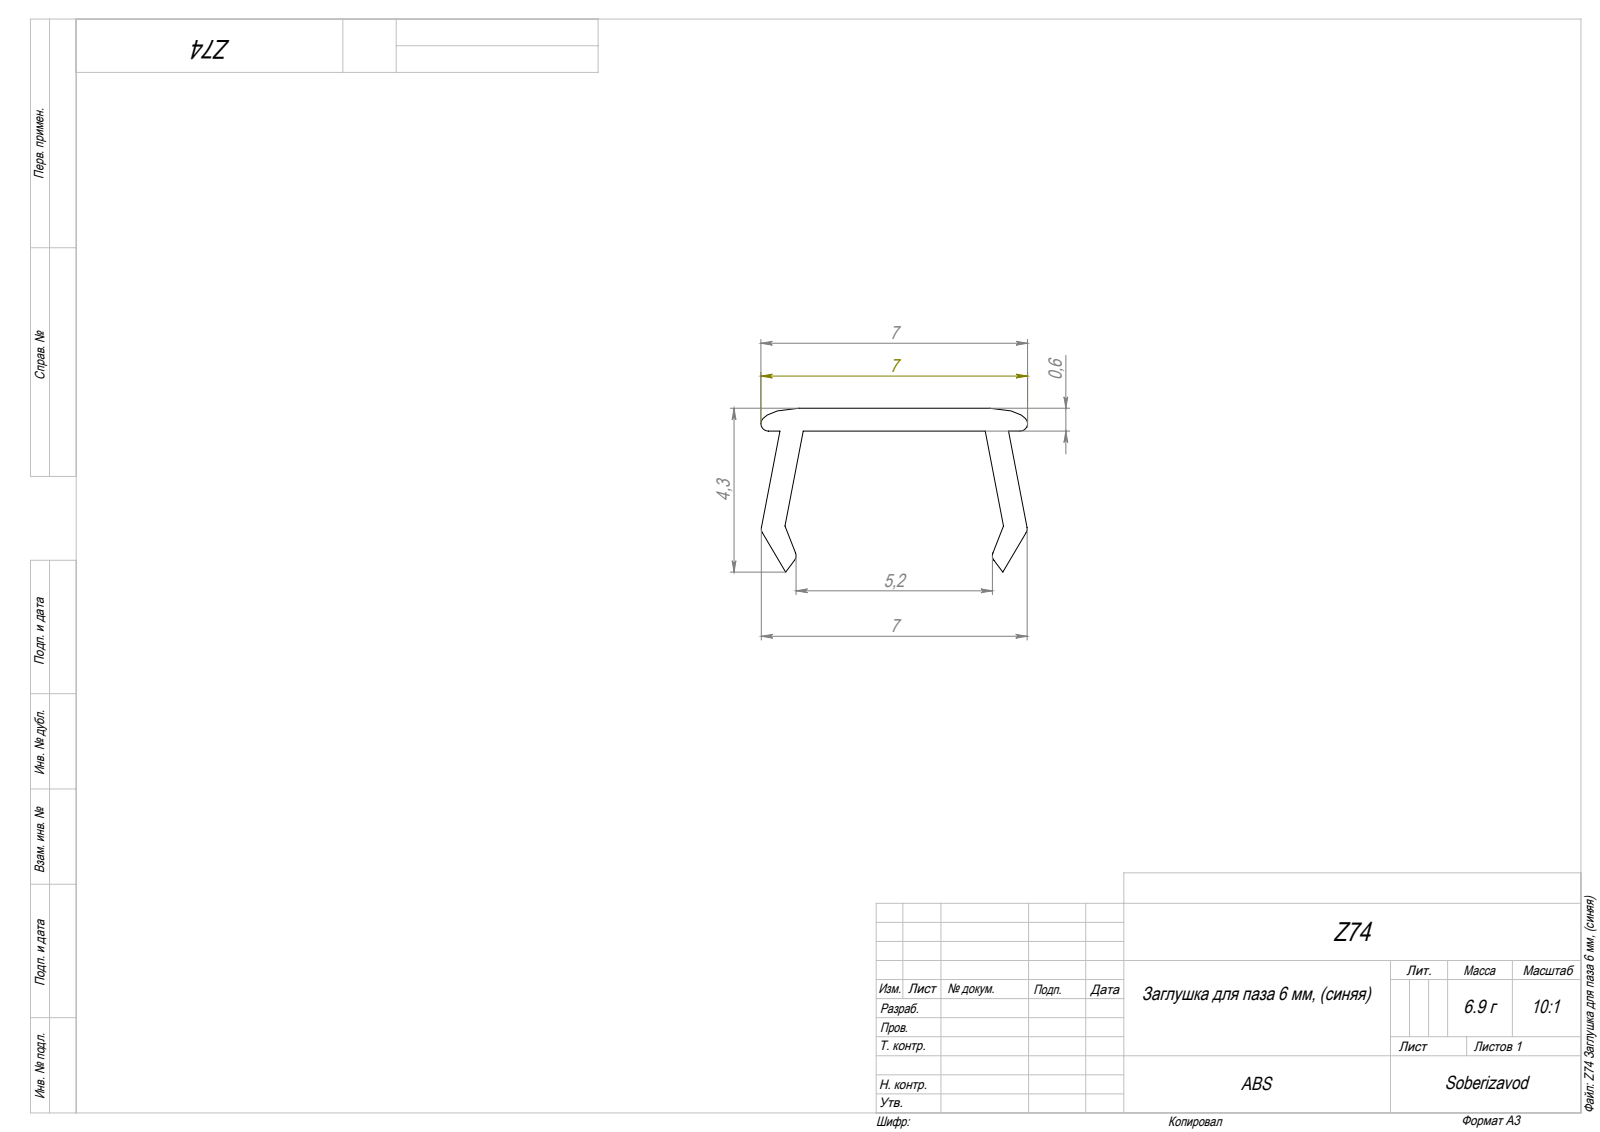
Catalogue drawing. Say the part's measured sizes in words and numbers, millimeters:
The part is named "Z74 Заглушка для паза 6 мм, (синяя)". Its 3-D file was written by "SolidWorks 2025 (AUTOMOTIVE_DESIGN)". It is 1 solid with 26 faces: 16 planar, 8 cylindrical and 2 other. Overall it measures 1000 by 7 by 4.3 millimeters. Its volume is 8 251 cubic millimeters and its surface area 28 934 square millimeters. Partial cylindrical surfaces (rounded edges, fillets, slot ends): 6 of radius 0.2. The main face-to-face distances are 0.6, 1000.
